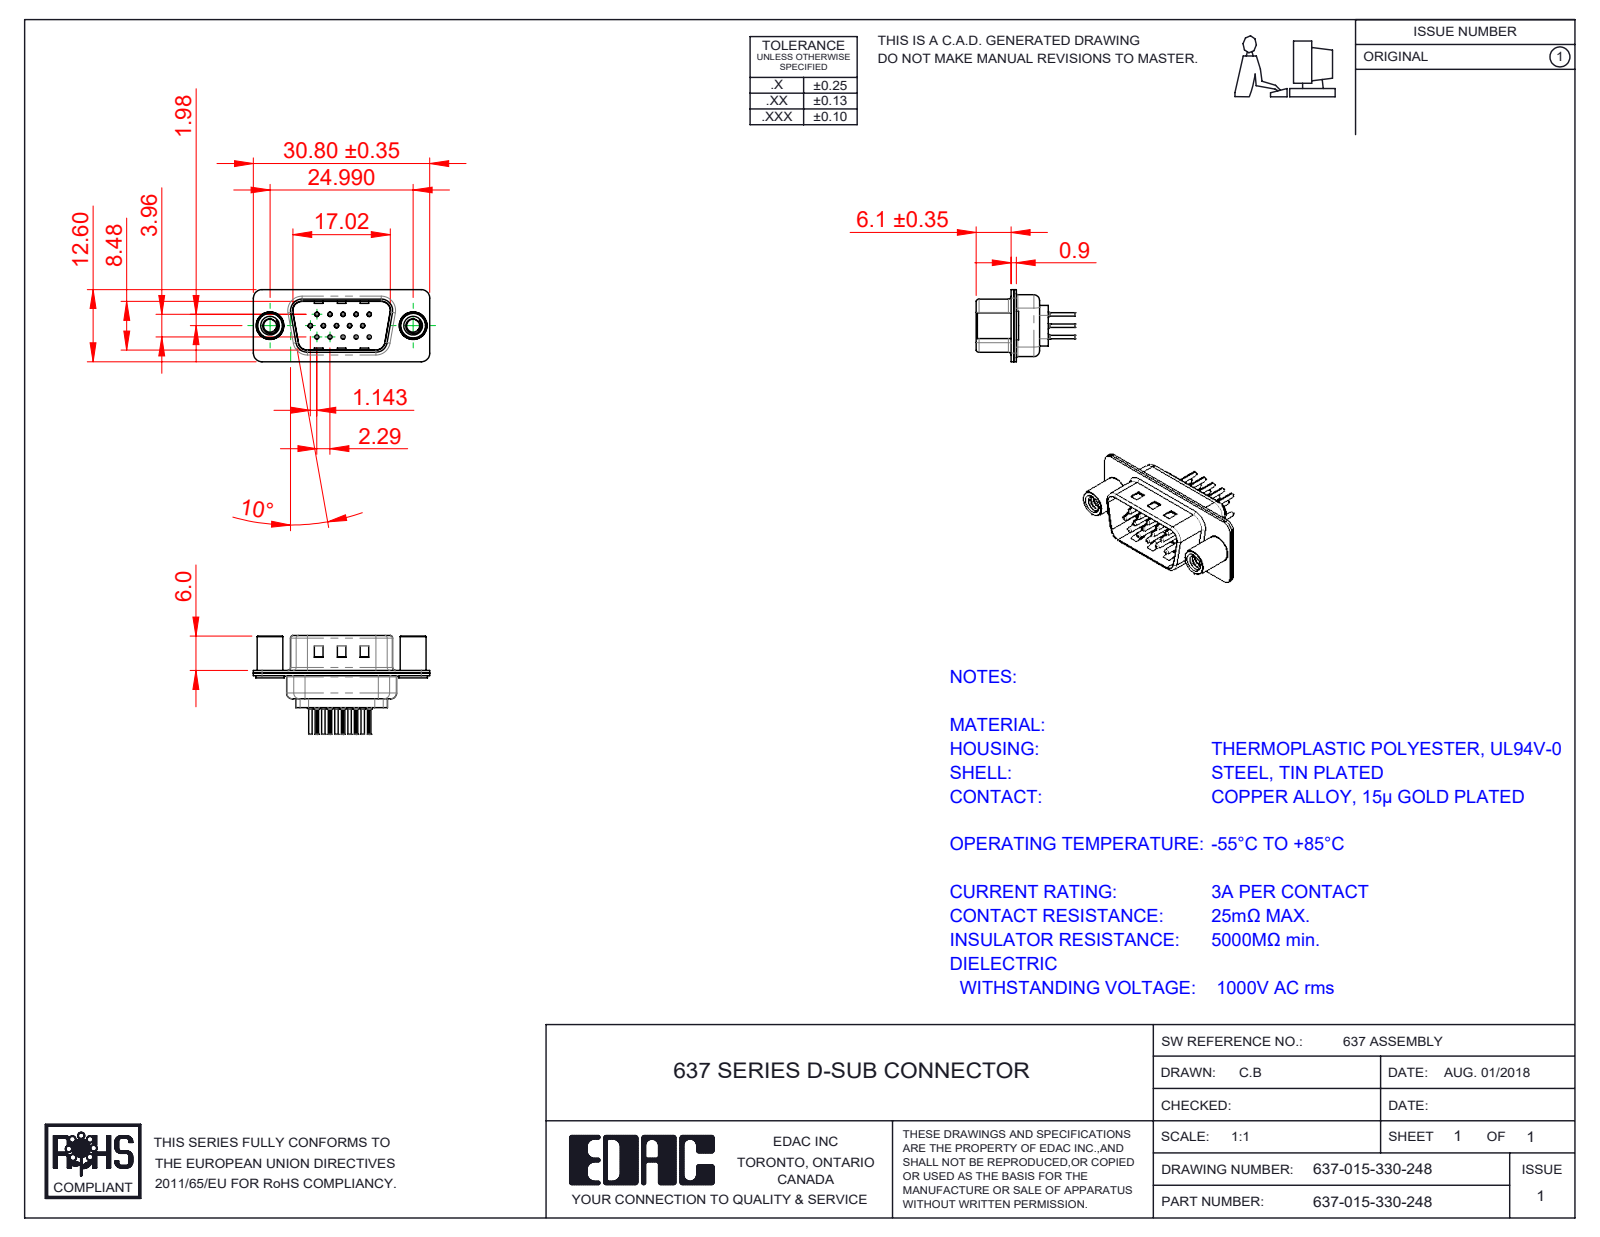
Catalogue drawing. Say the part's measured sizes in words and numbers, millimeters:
The part is named "637-015-330-248; 637 4-40 Threaded Standoff; 637 Housing_15 Contacts; 637 Shell Rear_15 Contacts (+4 more)". Its 3-D file was written by "SolidWorks 2020 (CONFIG_CONTROL_DESIGN)". It is 20 solids with 1838 faces: 469 planar, 712 cylindrical and 657 other. Overall it measures 30.8 by 17.25 by 12.6 millimeters. Its volume is 1 379 cubic millimeters and its surface area 4 840 square millimeters. Round holes: 15 of diameter 0.2, 15 of diameter 0.35, 15 of diameter 1.1, 15 of diameter 1.6, 2 of diameter 2.26, 2 of diameter 4, 2 of diameter 4.8. Round bosses or shafts: 15 of diameter 2, 15 of diameter 1.5, 15 of diameter 0.75, 15 of diameter 0.6, 2 of diameter 5, 2 of diameter 4.9, 2 of diameter 4.5. Partial cylindrical surfaces (rounded edges, fillets, slot ends): 30 of radius 0.1, 16 of radius 1.5, 12 of radius 2, 8 of radius 0.5, 4 of radius 0.25, 4 of radius 0.55, 4 of radius 0.7, 4 of radius 0.95. The main face-to-face distances are 0.45, 0.9, 0.4, 0.7, 8.88, 8.48, 1.05, 0.31, 4.55, 1.16. The hole center spacings are 3.96, 2.28, 4.57, 2.29, 6.05, 6.86, 7.92, 6.04.
